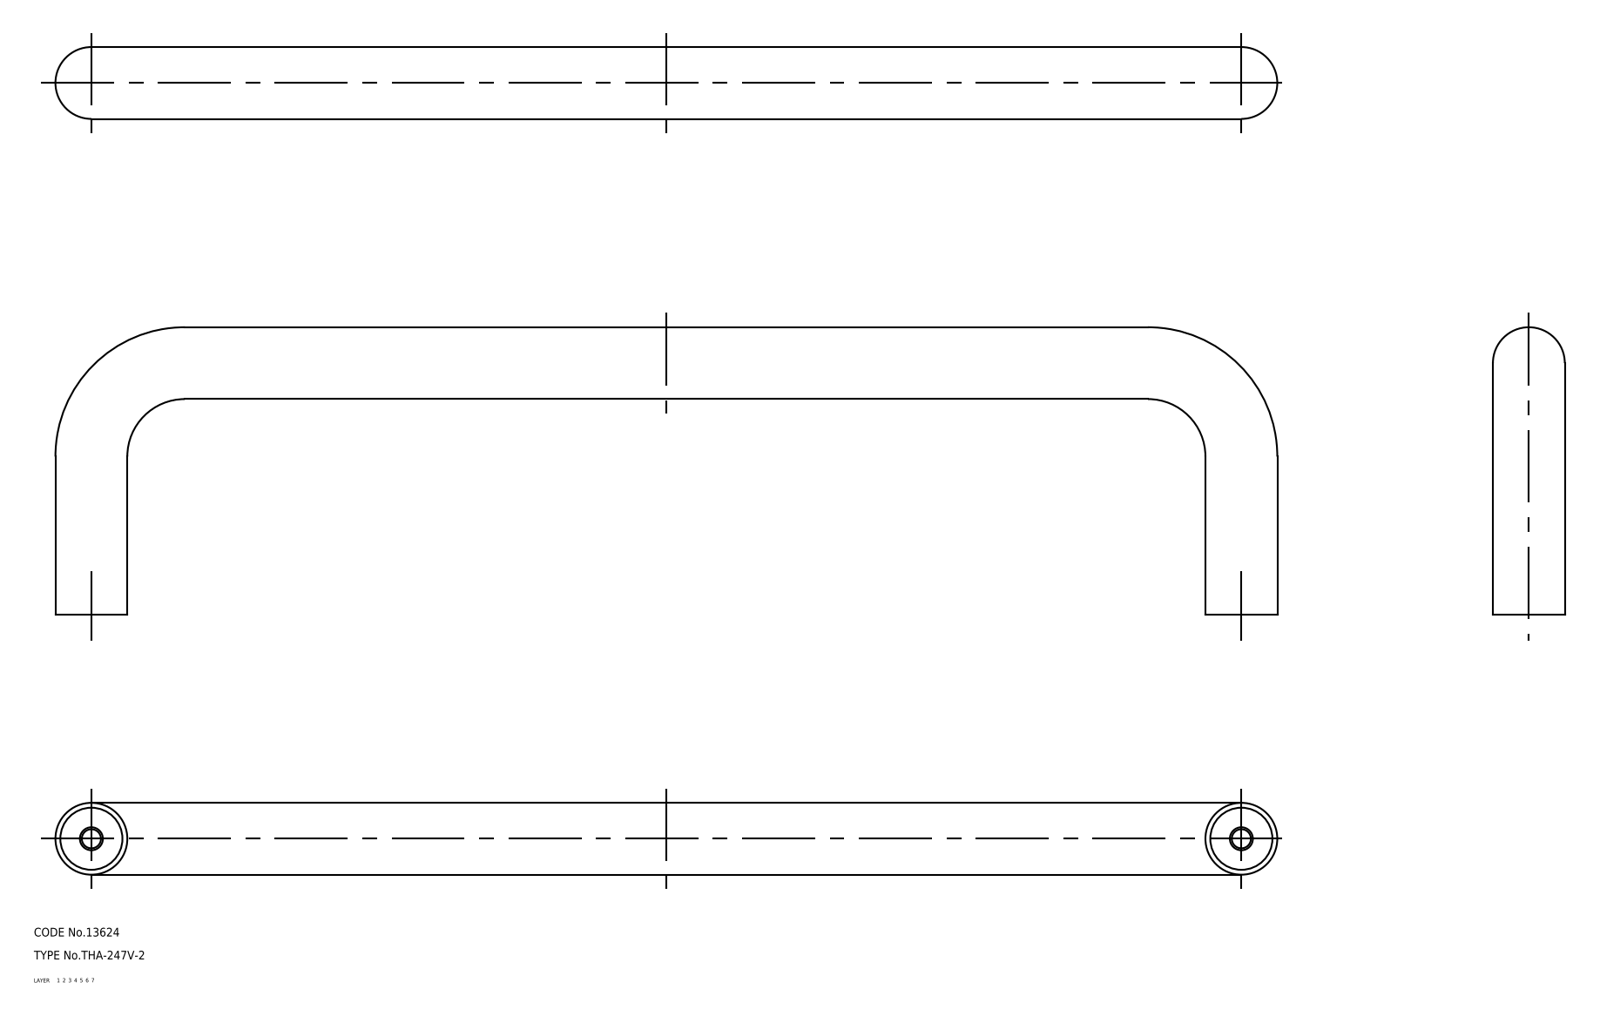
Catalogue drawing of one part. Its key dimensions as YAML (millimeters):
part_name: "67111314; 67111327; 67111340"
step_written_by: "CADfix (AUTOMOTIVE_DESIGN)"
units: millimeters
bodies: {solids: 3, faces: 34, planar: 0, cylindrical: 0, other: 34}
overall_size: [425, 100, 25]
volume: 78334
surface_area: 84680
